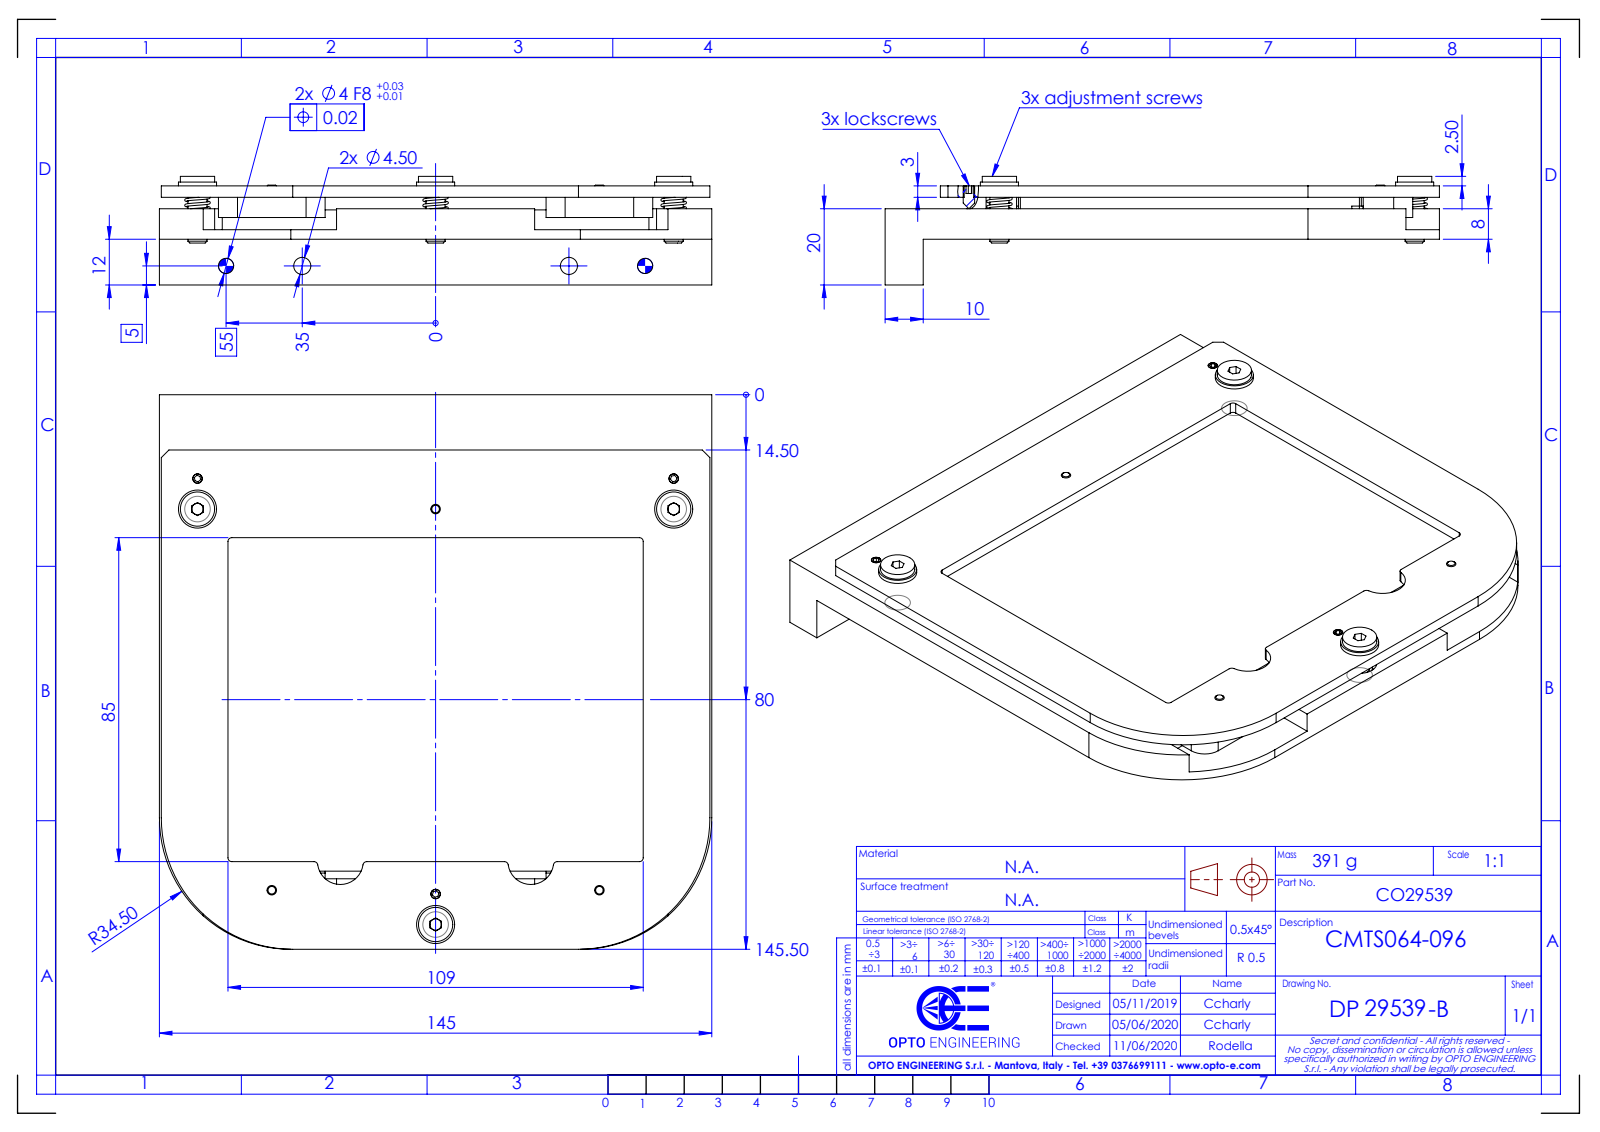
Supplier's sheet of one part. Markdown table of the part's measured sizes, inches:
| quantity | value |
| --- | --- |
| part name | DP29539-B_CMTS064-096 |
| STEP written by | SolidWorks 2021 (CONFIG_CONTROL_DESIGN) |
| units | inches |
| bodies | 0 solids, 227 faces (135 planar, 62 cylindrical, 30 other) |
| overall size | 5.728 × 5.709 × 1.122 |
| round holes (diameter × count) | 0.256 × 3, 0.157 × 2, 0.177 × 2, 0.098 × 1, 0.354 × 1 |
| round bosses / shafts (diameter × count) | 0.394 × 3, 0.197 × 3, 0.354 × 2, 0.118 × 1 |
| partial cylindrical surfaces (radius × count) | 0.039 × 8, 0.079 × 4, 0.197 × 4, 1.358 × 4, 0.157 × 2, 0.236 × 2 |
| main face-to-face distances | 0.118, 0.13, 0.551, 0.248, 0.433, 0.303, 0.236, 0.315, 0.571, 0.906 |
| hole center spacings | 0.787, 1.73, 3.543, 4.285, 2.756, 3.386, 4.291, 4.331 |
